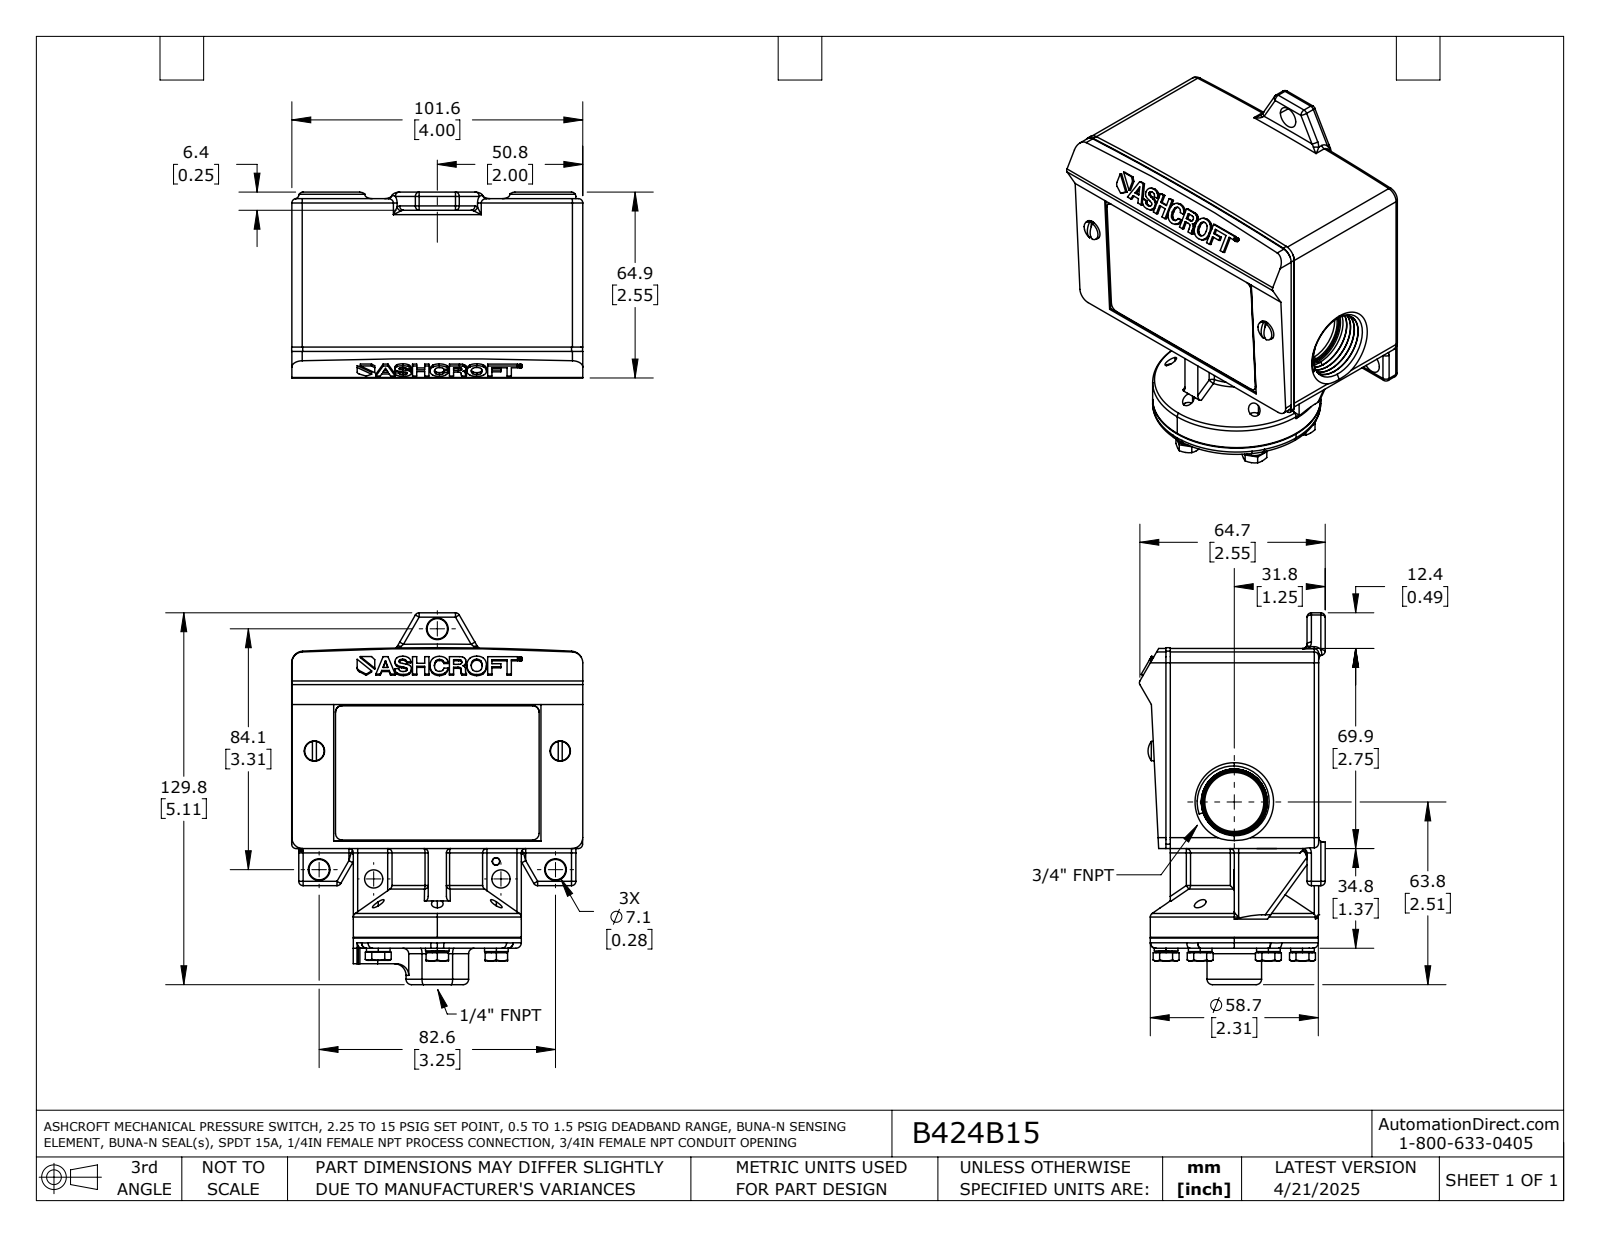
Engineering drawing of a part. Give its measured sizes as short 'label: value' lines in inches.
name: B424B15
written by: SolidWorks 2021 (AUTOMOTIVE_DESIGN)
unit: in
bodies: 2 solids, 1259 faces (345 planar, 472 cylindrical, 442 other)
size: 5.111 × 4.003 × 2.555
volume: 28.57 in³; area: 84.51 in²
holes: 6× ⌀0.161, 5× ⌀0.192, 5× ⌀0.209, 4× ⌀0.187, 2× ⌀0.28, 1× ⌀0.455, 1× ⌀0.812
bosses: 6× ⌀0.325, 6× ⌀0.278, 5× ⌀0.19, 2× ⌀0.27, 2× ⌀0.25, 1× ⌀2.31
rounds: 92× R0.06, 5× R0.03, 4× R0.075, 4× R0.09, 4× R0.15, 2× R0.01, 2× R0.094, 2× R0.16
face distances: 4, 0.015, 1.37, 0.09, 3.91, 0.44, 3.56, 3.47, 0.35, 0.845
hole spacings: 0.937, 1.624, 1.875, 0.938, 3.38
